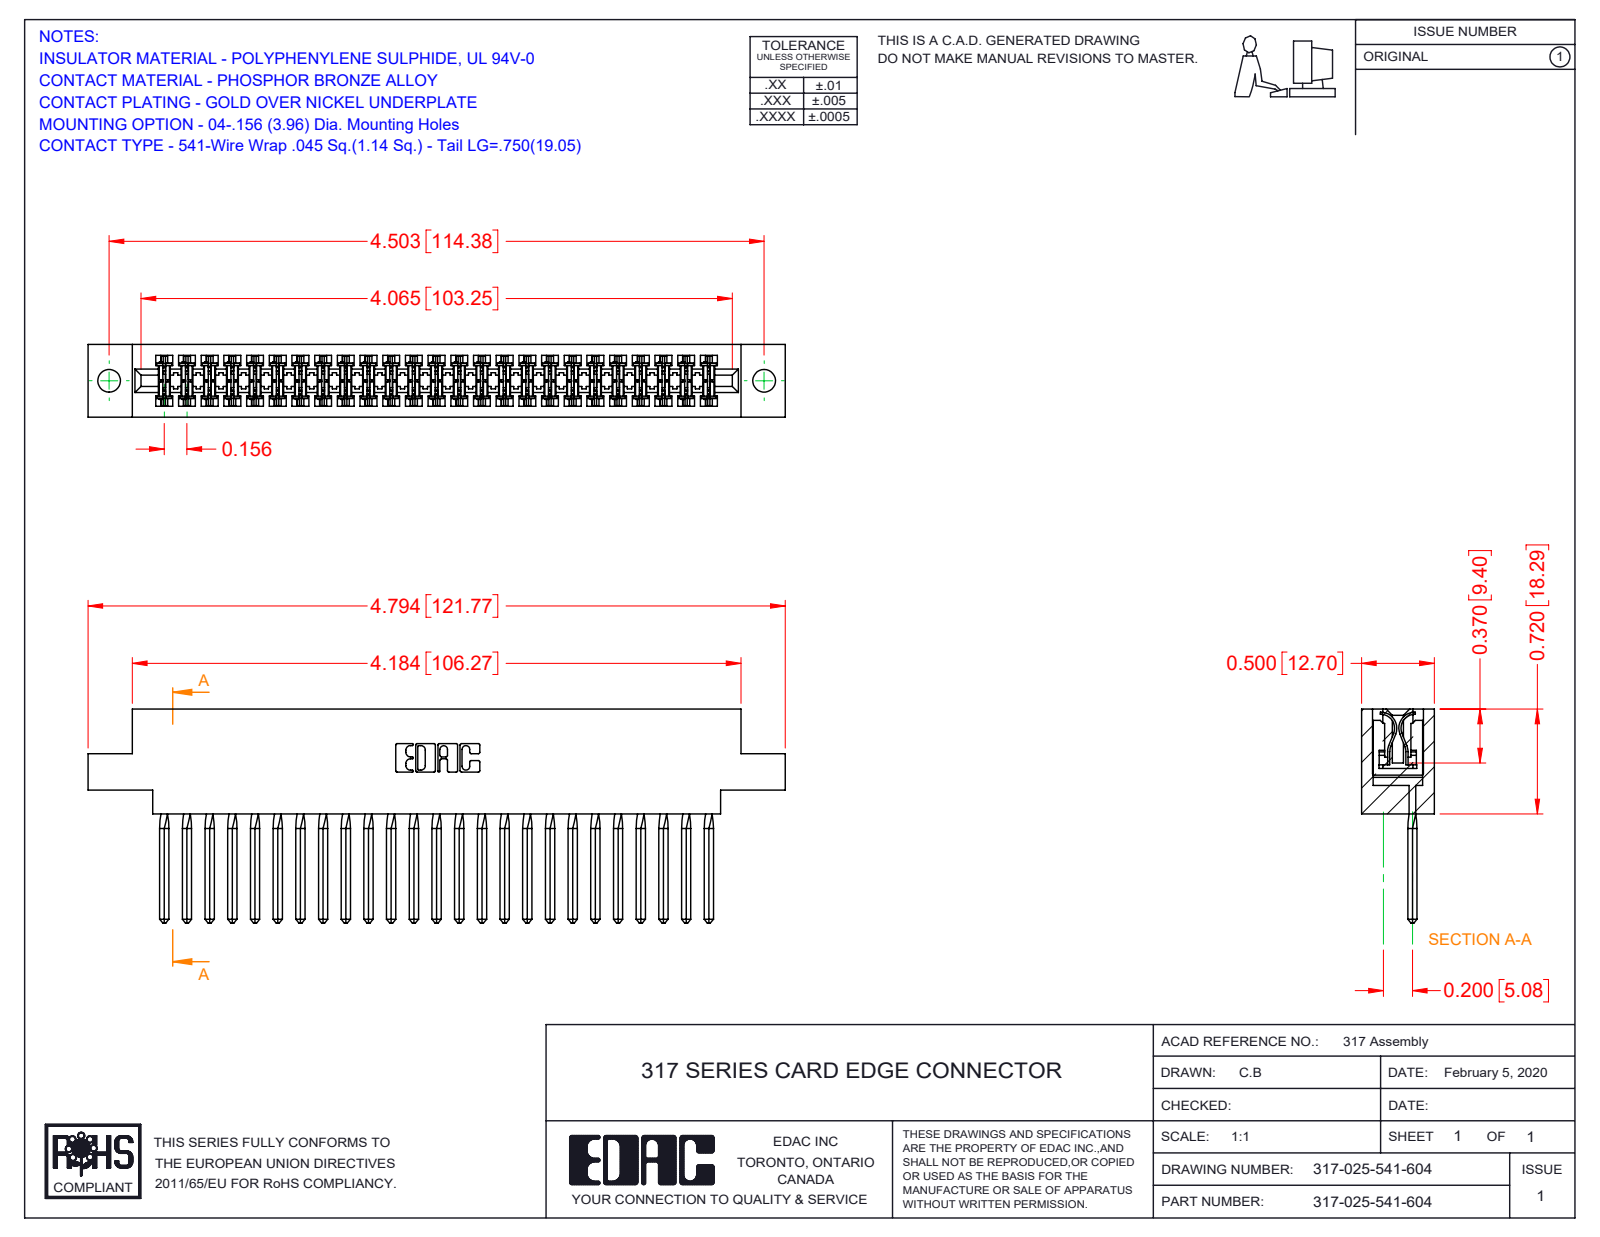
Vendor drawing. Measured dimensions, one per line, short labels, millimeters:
name: 317 Part_.156 Dia - TH; 317-025-541-604; 317-290-002_541
written by: SolidWorks 2016 (CONFIG_CONTROL_DESIGN)
unit: mm
bodies: 26 solids, 3902 faces (3158 planar, 644 cylindrical, 100 other)
size: 121.8 × 37.3 × 12.7
volume: 19 140 mm³; area: 26 290 mm²
holes: 2× ⌀4
rounds: 50× R0.4, 22× R0.3, 6× R0.2, 6× R0.8, 3× R0.7, 2× R2.4, 2× R2.5, 2× R2.8
face distances: 12.7, 1.9, 10.8, 8.9, 2.8, 5, 18.3, 19.6, 5.6, 5.4
hole spacings: 114.4
